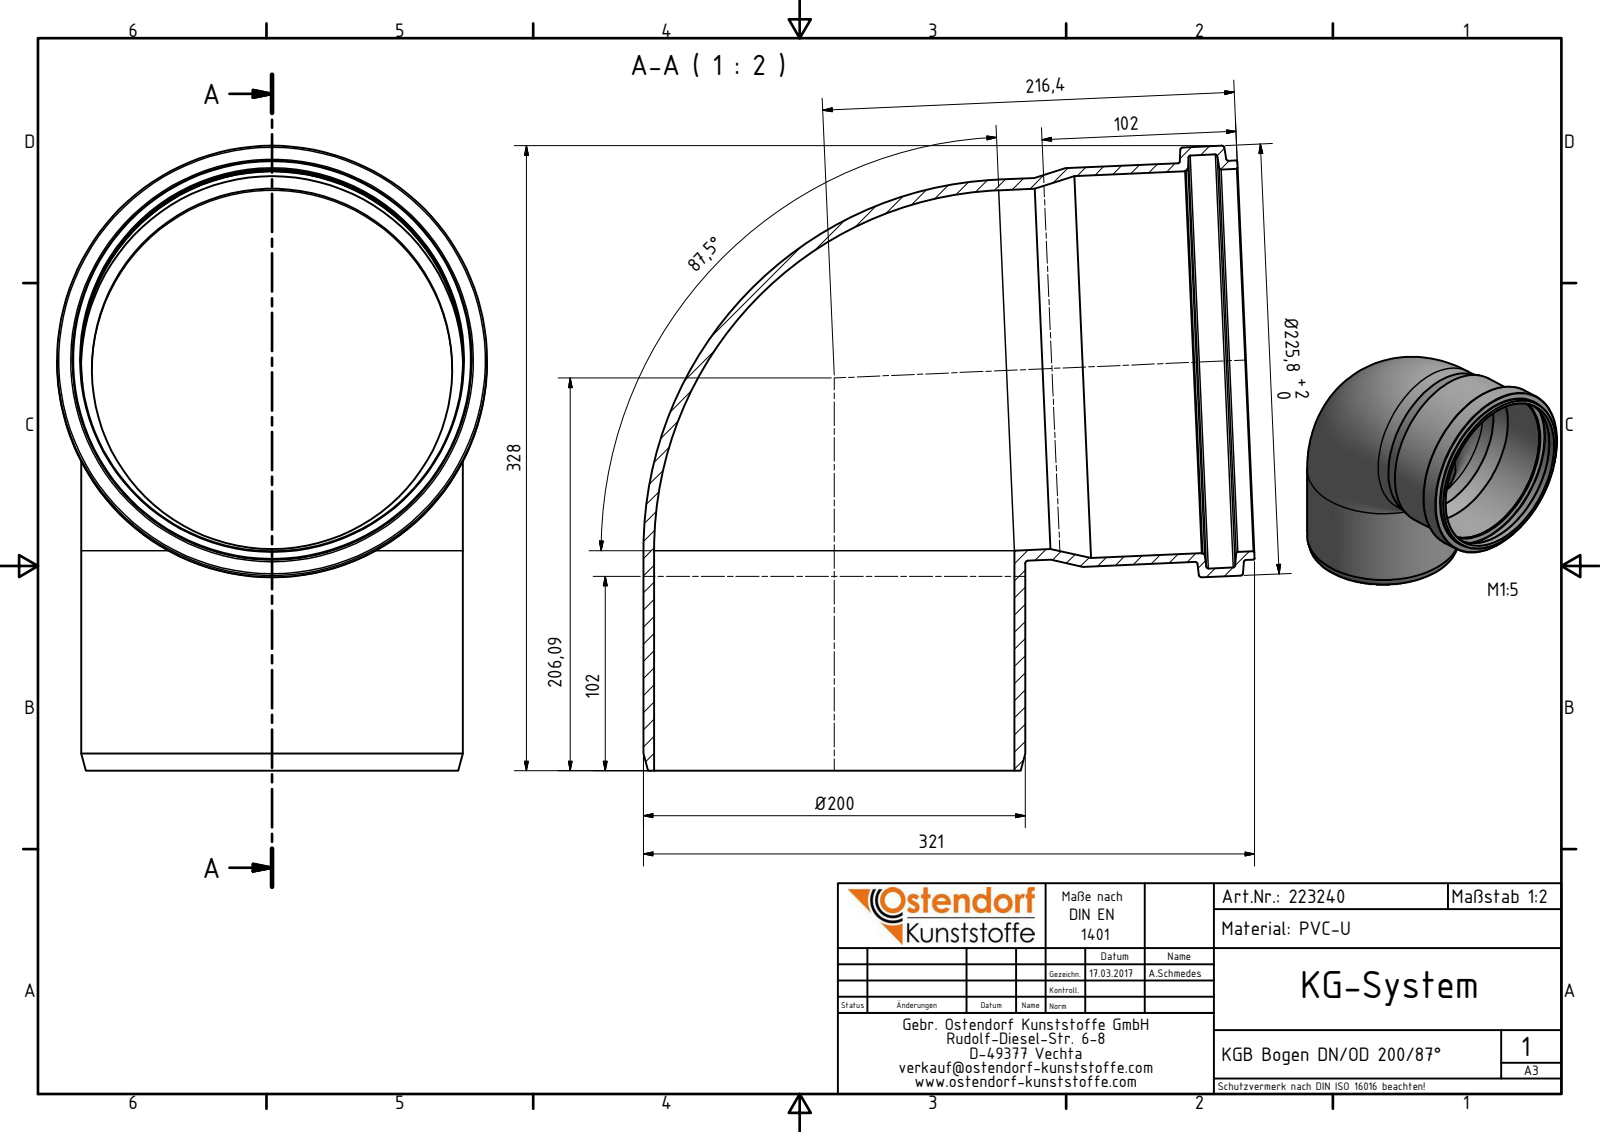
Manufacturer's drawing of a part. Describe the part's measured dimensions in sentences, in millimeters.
The part is named "223240 KGB Bogen DN_OD 200_87°". Its 3-D file was written by "Autodesk Inventor 2016 (AUTOMOTIVE_DESIGN)". It is 1 solid with 34 faces: 3 planar, 11 cylindrical and 20 other. Overall it measures 328 by 321 by 225.8 millimeters. Its volume is 1 147 000 cubic millimeters and its surface area 504 255 square millimeters. Round holes: 2 of diameter 189.3, 2 of diameter 200.9, 1 of diameter 200.6, 1 of diameter 217. Round bosses or shafts: 2 of diameter 200.5, 1 of diameter 225.8, 1 of diameter 209.7, 1 of diameter 209.4. The main face-to-face distances are 27.57.
